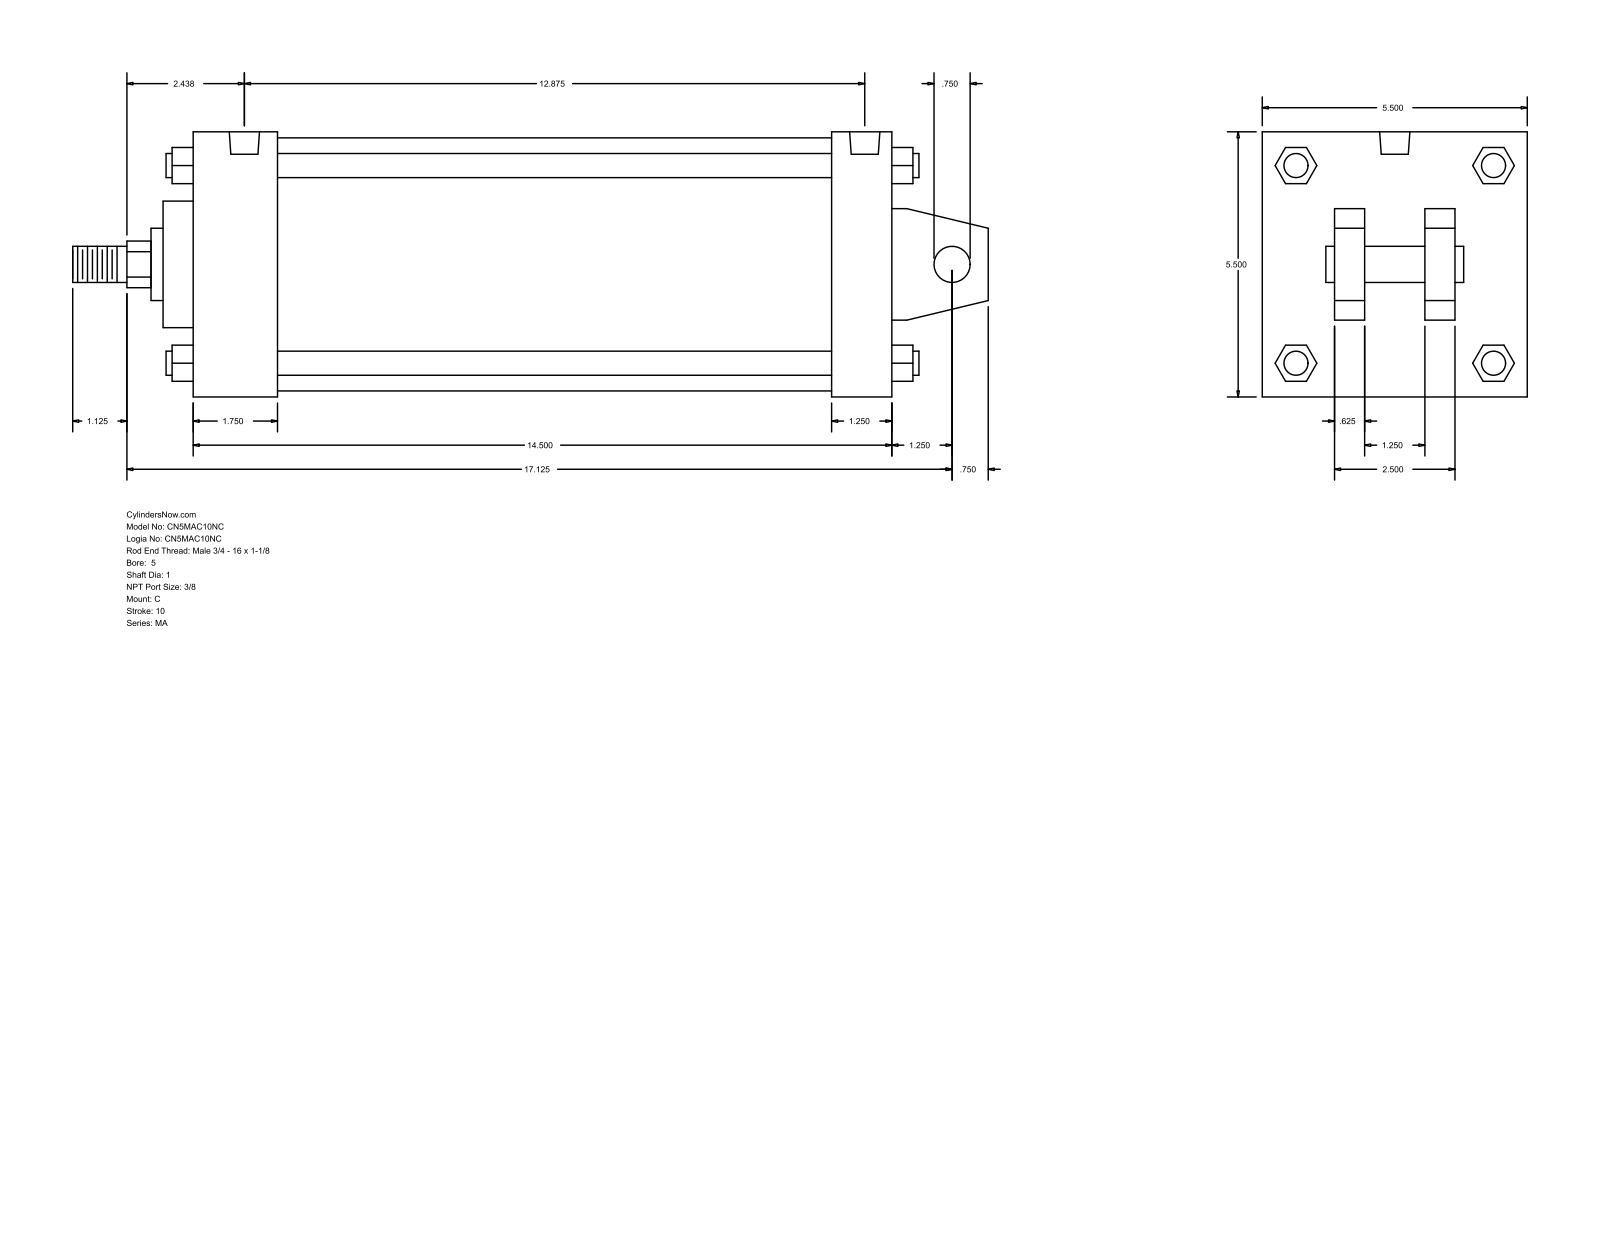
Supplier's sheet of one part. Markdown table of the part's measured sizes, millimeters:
| quantity | value |
| --- | --- |
| part name | MA_C__0500_1 |
| STEP written by | GSSL Pune (CONFIG_CONTROL_DESIGN) |
| units | millimeters |
| bodies | 0 solids, 141 faces (109 planar, 32 cylindrical, 0 other) |
| overall size | 482.6 × 139.7 × 139.7 |
| round holes (diameter × count) | 11.11 × 4, 15.93 × 2 |
| round bosses / shafts (diameter × count) | 12.7 × 4, 19.05 × 2, 133.35 × 1, 66.67 × 1, 38.1 × 1, 25.4 × 1 |
| partial cylindrical surfaces (radius × count) | 12.29 × 1 |
| main face-to-face distances | 139.7, 368.31, 15.87, 336.56, 31.75, 44.46, 292.1, 323.85, 38.1, 101.6 |
| hole center spacings | 4.76, 317.51, 322.27, 327.03 |
